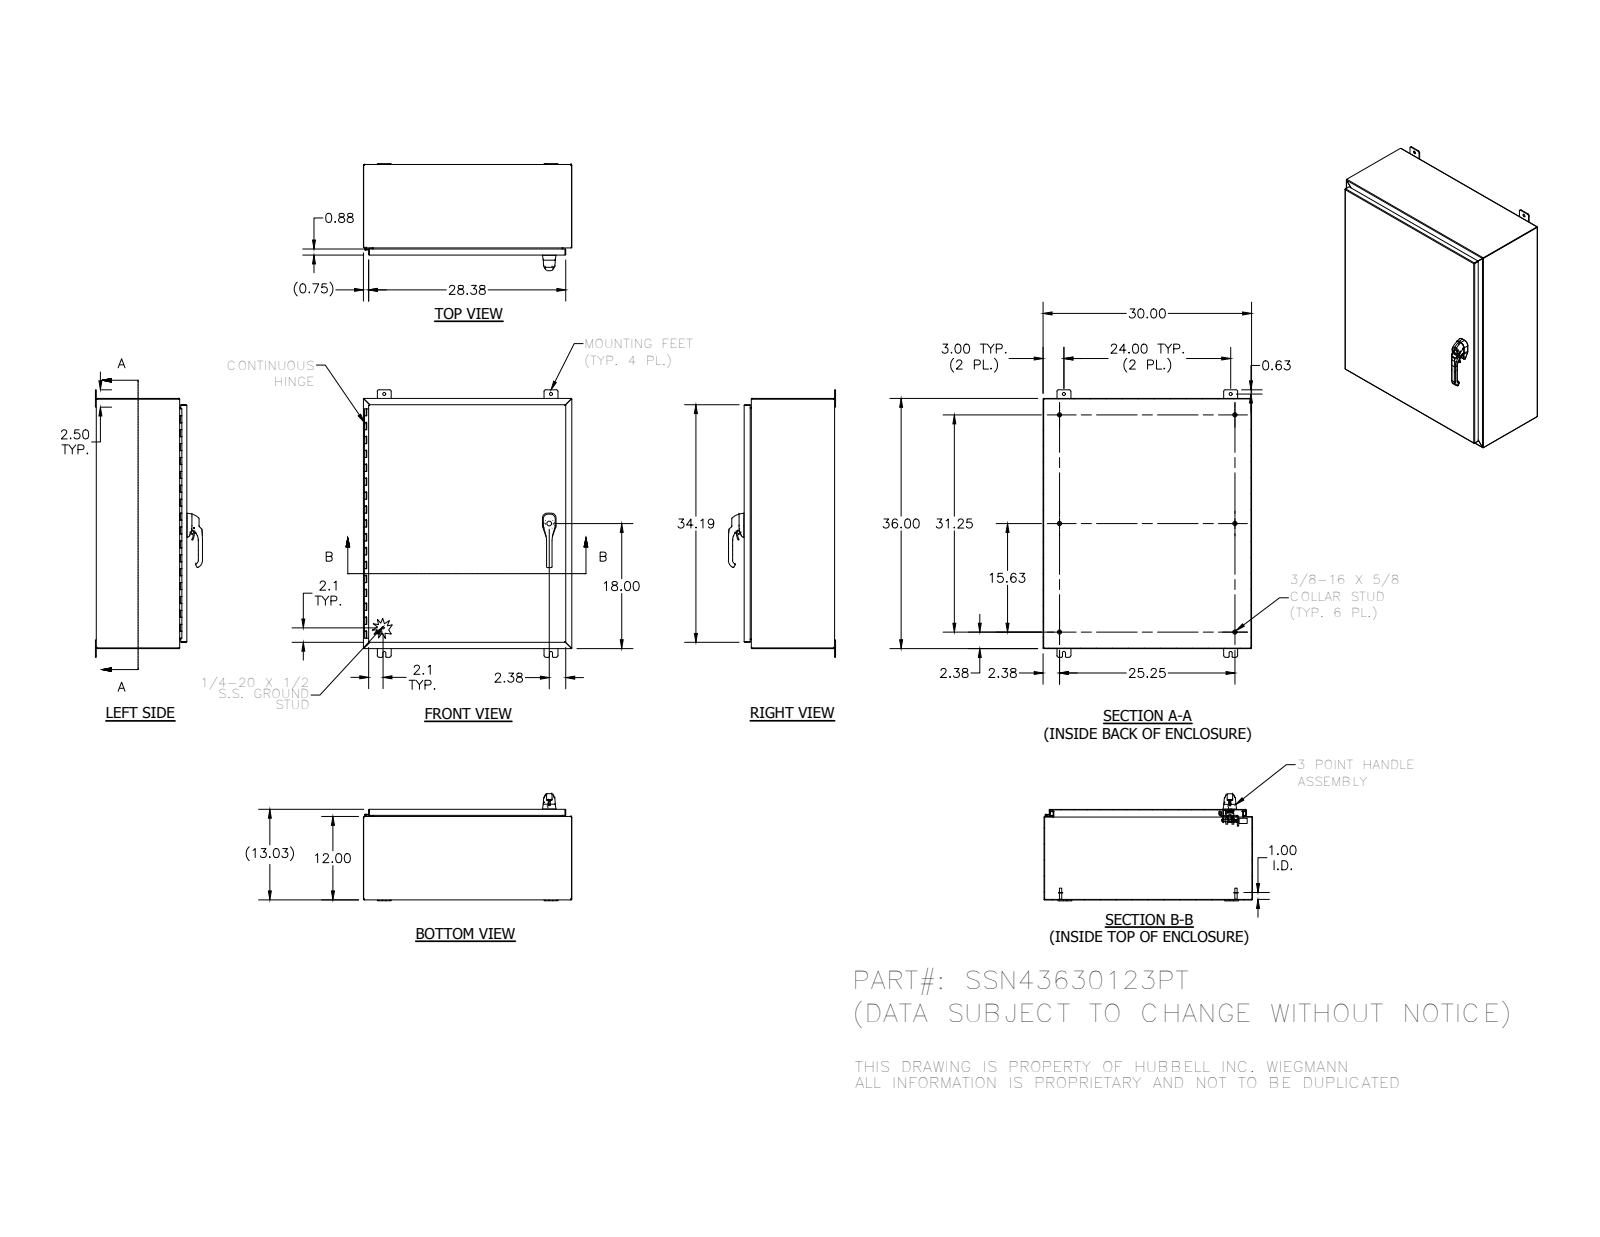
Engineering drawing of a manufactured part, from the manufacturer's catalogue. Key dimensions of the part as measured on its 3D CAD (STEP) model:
Part name (STEP PRODUCT): HFW369101; 1000-02; 1091-903_AF0; D125B_10_5 (+8 more)
STEP written by: SolidWorks 2014 (AUTOMOTIVE_DESIGN)
Units: inches
Bodies: 57 solids, 3191 faces (1086 planar, 1328 cylindrical, 777 other)
Overall size (bounding box): 38.5 × 30 × 15.408
Volume: 318 in³ · Surface area: 8 525 in²
Round holes (diameter × count): ⌀0.262 ×8, ⌀0.187 ×4, ⌀0.438 ×4, ⌀0.213 ×3, ⌀0.281 ×3, ⌀0.241 ×2, ⌀0.25 ×2, ⌀0.252 ×2, ⌀0.315 ×2, ⌀0.4 ×2, ⌀0.402 ×2, ⌀0.413 ×2
Round bosses / shafts (diameter × count): ⌀0.625 ×6, ⌀0.33 ×6, ⌀0.236 ×3, ⌀1 ×2, ⌀0.563 ×2, ⌀0.533 ×2, ⌀0.531 ×2, ⌀0.5 ×2
Partial cylindrical surfaces — rounded edges, fillets, slot ends (radius × count): R0.02 ×172, R0.012 ×113, R0.031 ×24, R0.019 ×21, R0.105 ×20, R0.25 ×20, R0.125 ×18, R0.025 ×16
Main face-to-face distances: 0.074, 12.959, 12.885, 13.033, 29.926, 35.926, 29.852, 30, 35.852, 36
Hole centre spacings: 0.38, 0.492, 0.76, 0.886, 26.428, 0.234, 0.258, 0.38
